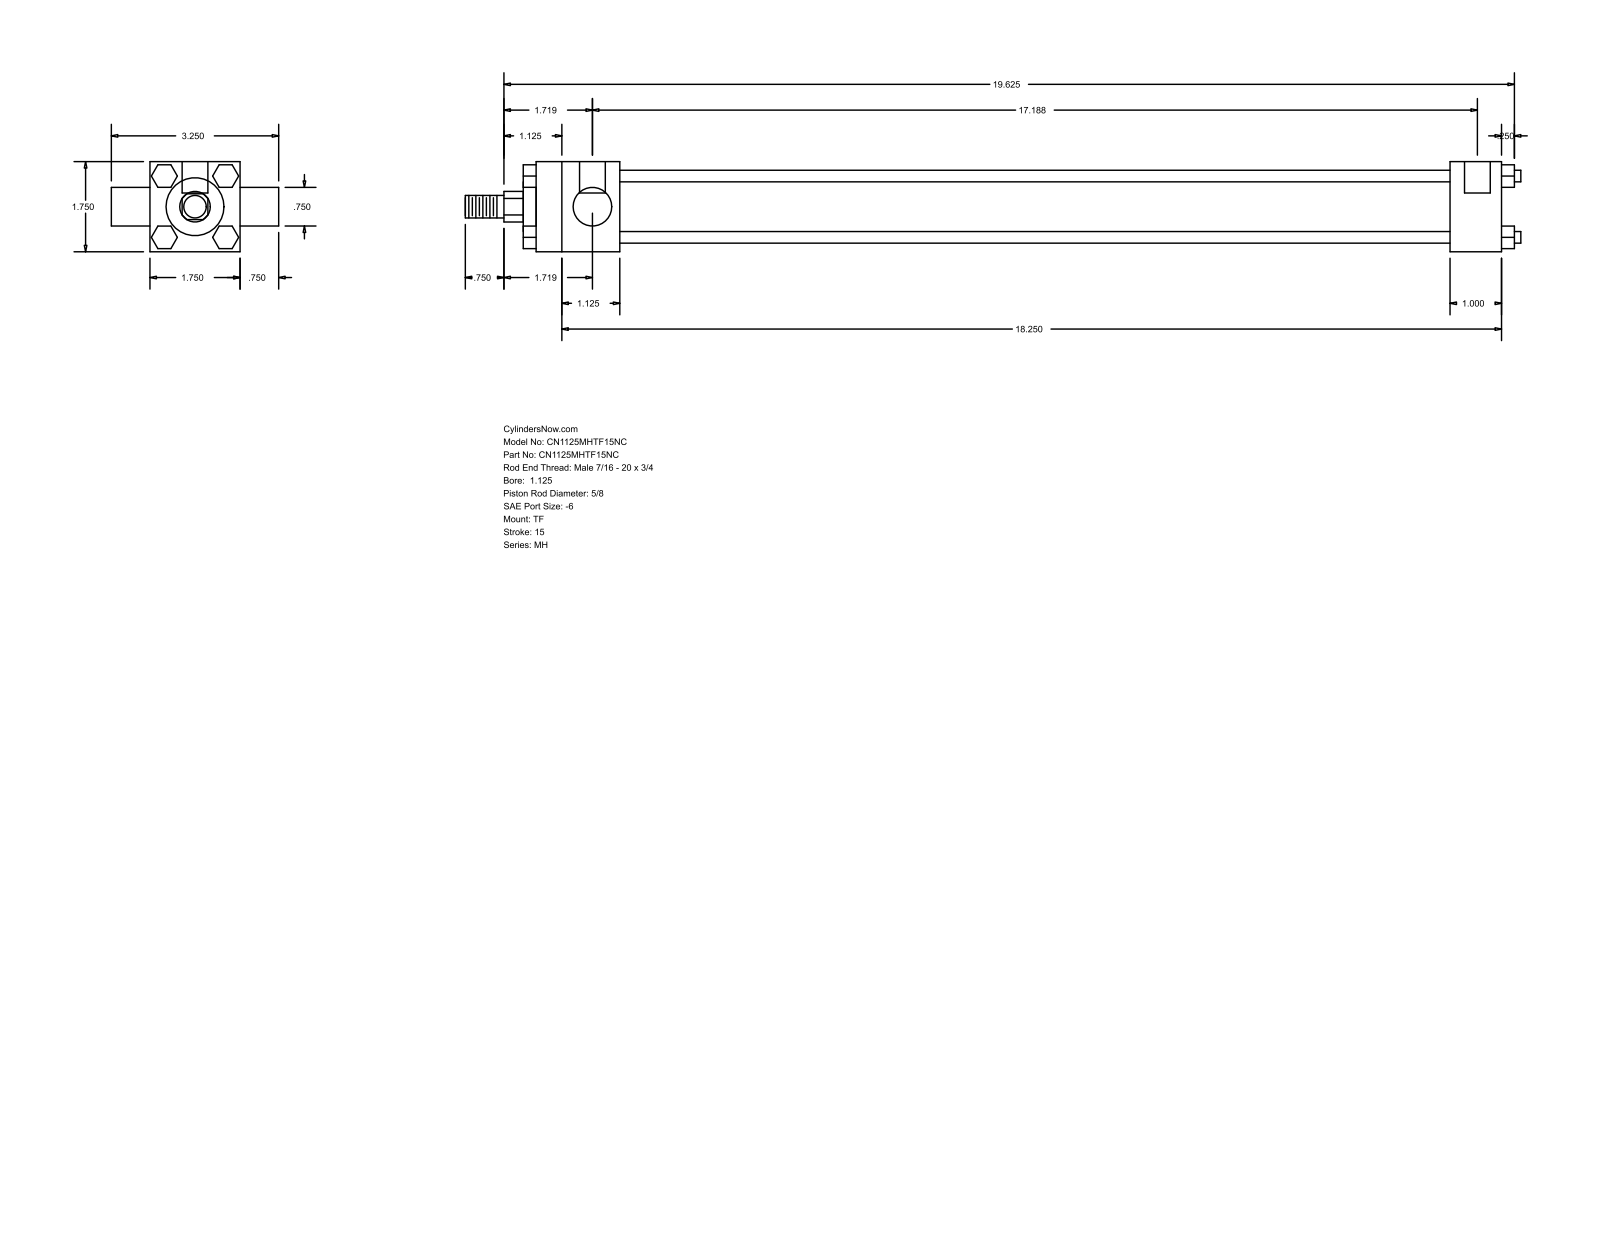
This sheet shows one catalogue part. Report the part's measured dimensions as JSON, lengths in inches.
{"part_name": "MH_TF__0112_0.625", "step_written_by": "GSSL Pune (CONFIG_CONTROL_DESIGN)", "units": "inches", "bodies": {"solids": 0, "faces": 120, "planar": 92, "cylindrical": 28, "other": 0}, "overall_size": [20.5, 3.25, 1.75], "round_holes": [[0.219, 3], [0.5, 2]], "round_bosses_or_shafts": [[0.225, 4], [1.375, 1], [1.125, 1], [0.75, 1], [0.625, 1], [0.437, 1]], "partial_cylinders_radius": [[0.297, 1]], "face_to_face_distances": [1.75, 0.437, 16.125, 17.125, 1, 1.625, 17.75, 18.75, 1.875, 0.25], "hole_center_spacings": [0.125, 17.063, 17.187]}
